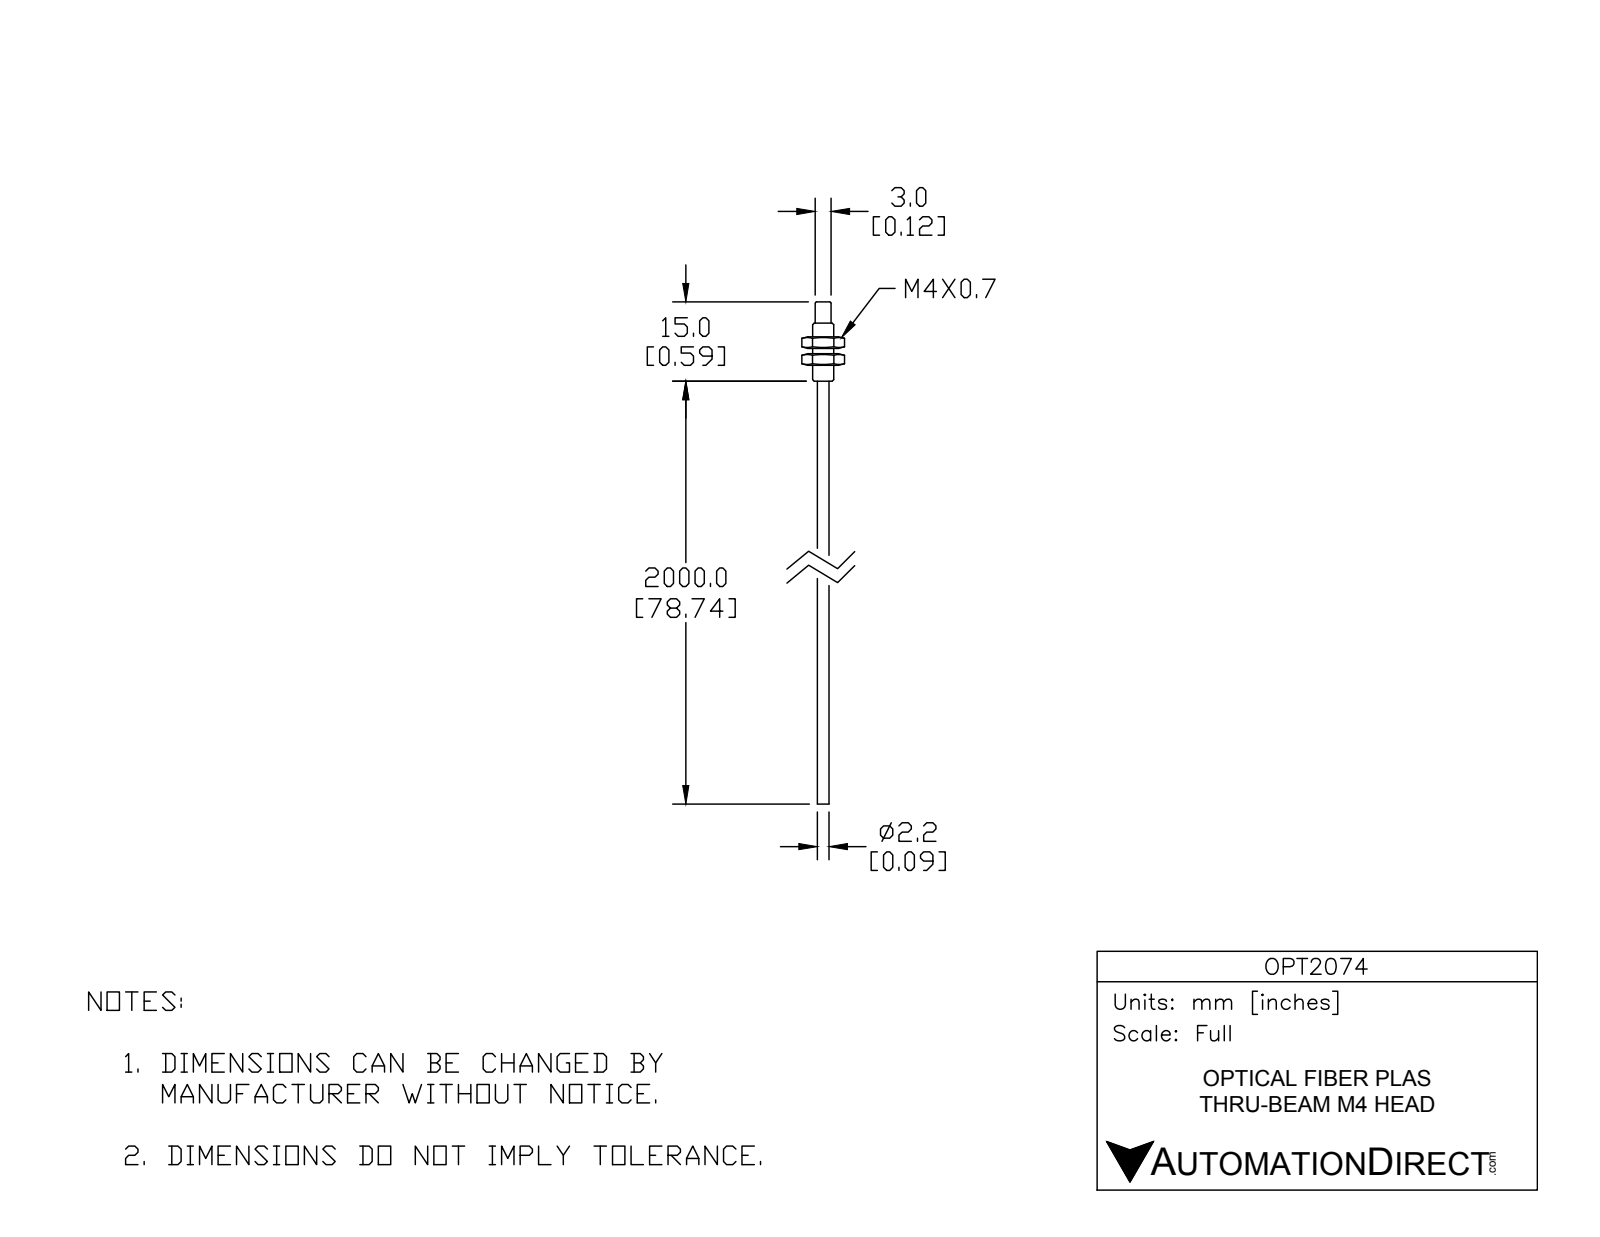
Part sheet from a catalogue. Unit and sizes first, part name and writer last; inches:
Units: inches
Overall size (bounding box): 3.74 × 0.318 × 0.276
Round bosses / shafts (diameter × count): ⌀0.157 ×1, ⌀0.118 ×1, ⌀0.087 ×1
Main face-to-face distances: 0.276, 0.087, 0.126, 0.213, 0.039, 0.26, 0.346, 0.386, 0.472, 0.591
Volume: 0.035 in³ · Surface area: 1.334 in²
Bodies: 2 solids, 48 faces (22 planar, 12 cylindrical, 14 other)
Part name (STEP PRODUCT): OPT2074
STEP written by: SolidWorks 2014 (AUTOMOTIVE_DESIGN)
